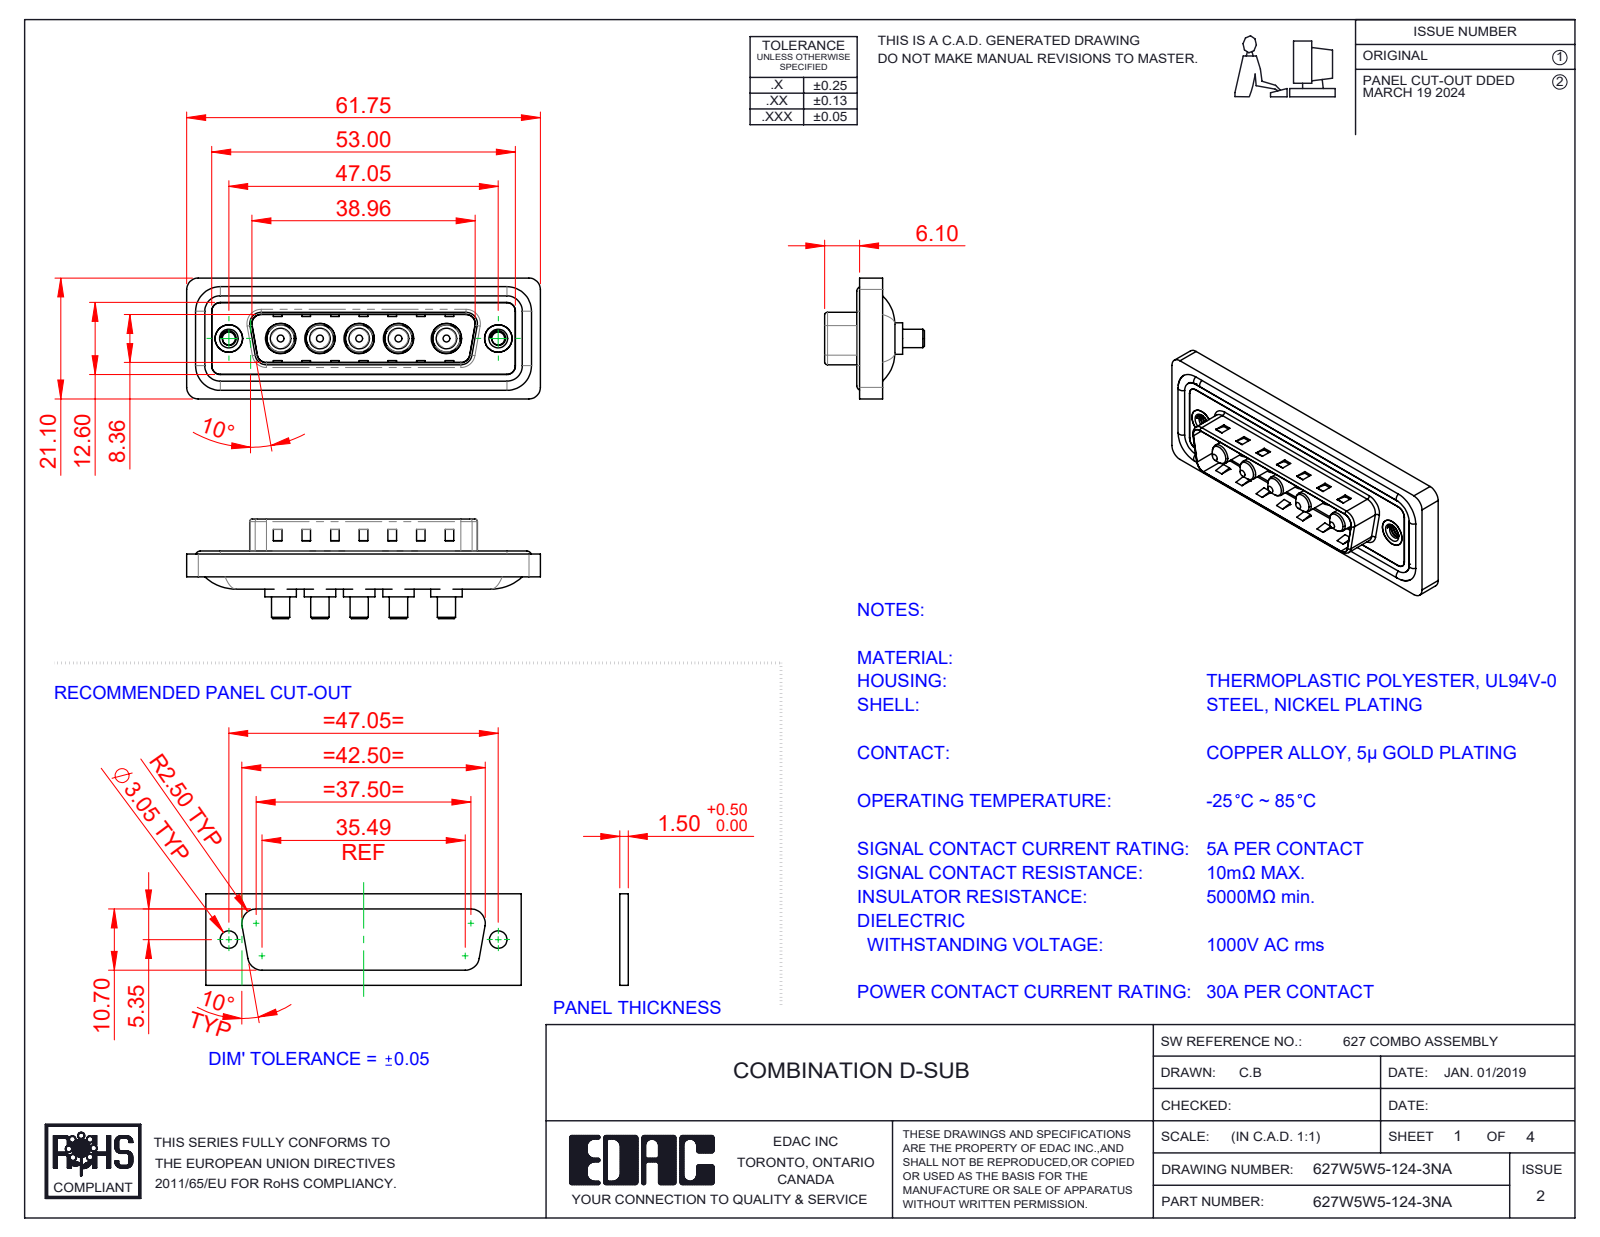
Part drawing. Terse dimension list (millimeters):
name: 627Combo Shell Rear_25 Contacts; 627Combo Housing_5W5; 627Combo Threaded Rivet_A; Power Pin_30A S (+3 more)
written by: SolidWorks 2023 (CONFIG_CONTROL_DESIGN)
unit: mm
bodies: 17 solids, 676 faces (259 planar, 285 cylindrical, 132 other)
size: 61.75 × 21.1 × 17.4
volume: 7 510 mm³; area: 11 817 mm²
holes: 5× ⌀4.85, 5× ⌀5.3, 2× ⌀2.26, 2× ⌀4, 2× ⌀4.8, 2× ⌀5
bosses: 5× ⌀5.5, 5× ⌀5.2, 5× ⌀4.75, 5× ⌀3.75, 5× ⌀3.6, 5× ⌀3.2, 4× ⌀1.6, 2× ⌀4.9
rounds: 22× R1.5, 18× R2, 8× R0.5, 8× R1.6, 5× R2.1, 4× R0.25, 4× R0.6, 4× R0.65
face distances: 0.4, 1.5, 0.5, 1.1, 3.1, 1.6, 2.9, 0.82, 9.58, 5.65
hole spacings: 6.86, 9.04, 13.73, 38.01, 6.87, 8.37, 8.38, 9.05
